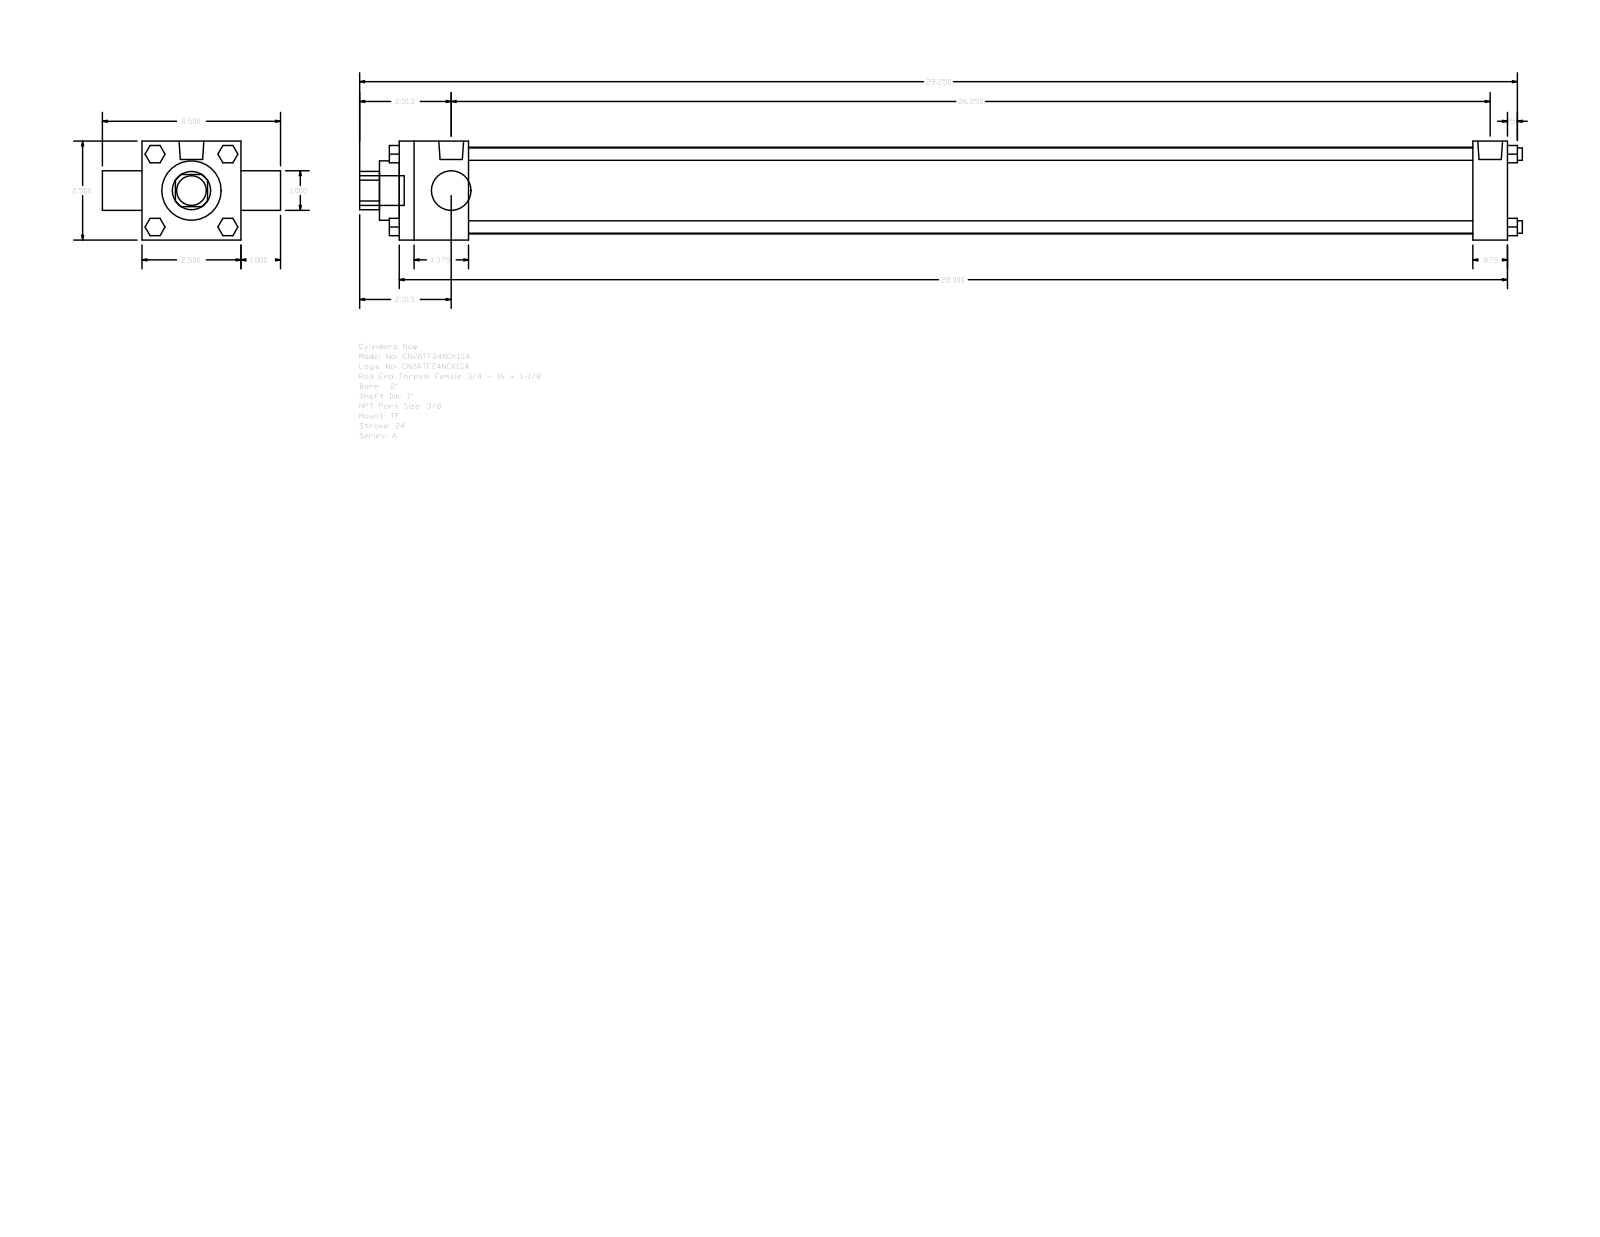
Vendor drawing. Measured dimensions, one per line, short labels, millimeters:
name: A_TF__0200_1
written by: GSSL Pune (CONFIG_CONTROL_DESIGN)
unit: mm
bodies: 0 solids, 120 faces (92 planar, 28 cylindrical, 0 other)
size: 746.12 × 114.3 × 63.5
holes: 2× ⌀25.4, 1× ⌀38.1, 1× ⌀55.63
bosses: 4× ⌀7.94, 3× ⌀5.56, 2× ⌀15.93, 1× ⌀19.05
rounds: 1× R12.29
face distances: 63.5, 711.2, 44.45, 688.98, 644.53, 666.75, 22.22, 25.4, 88.9, 723.9
